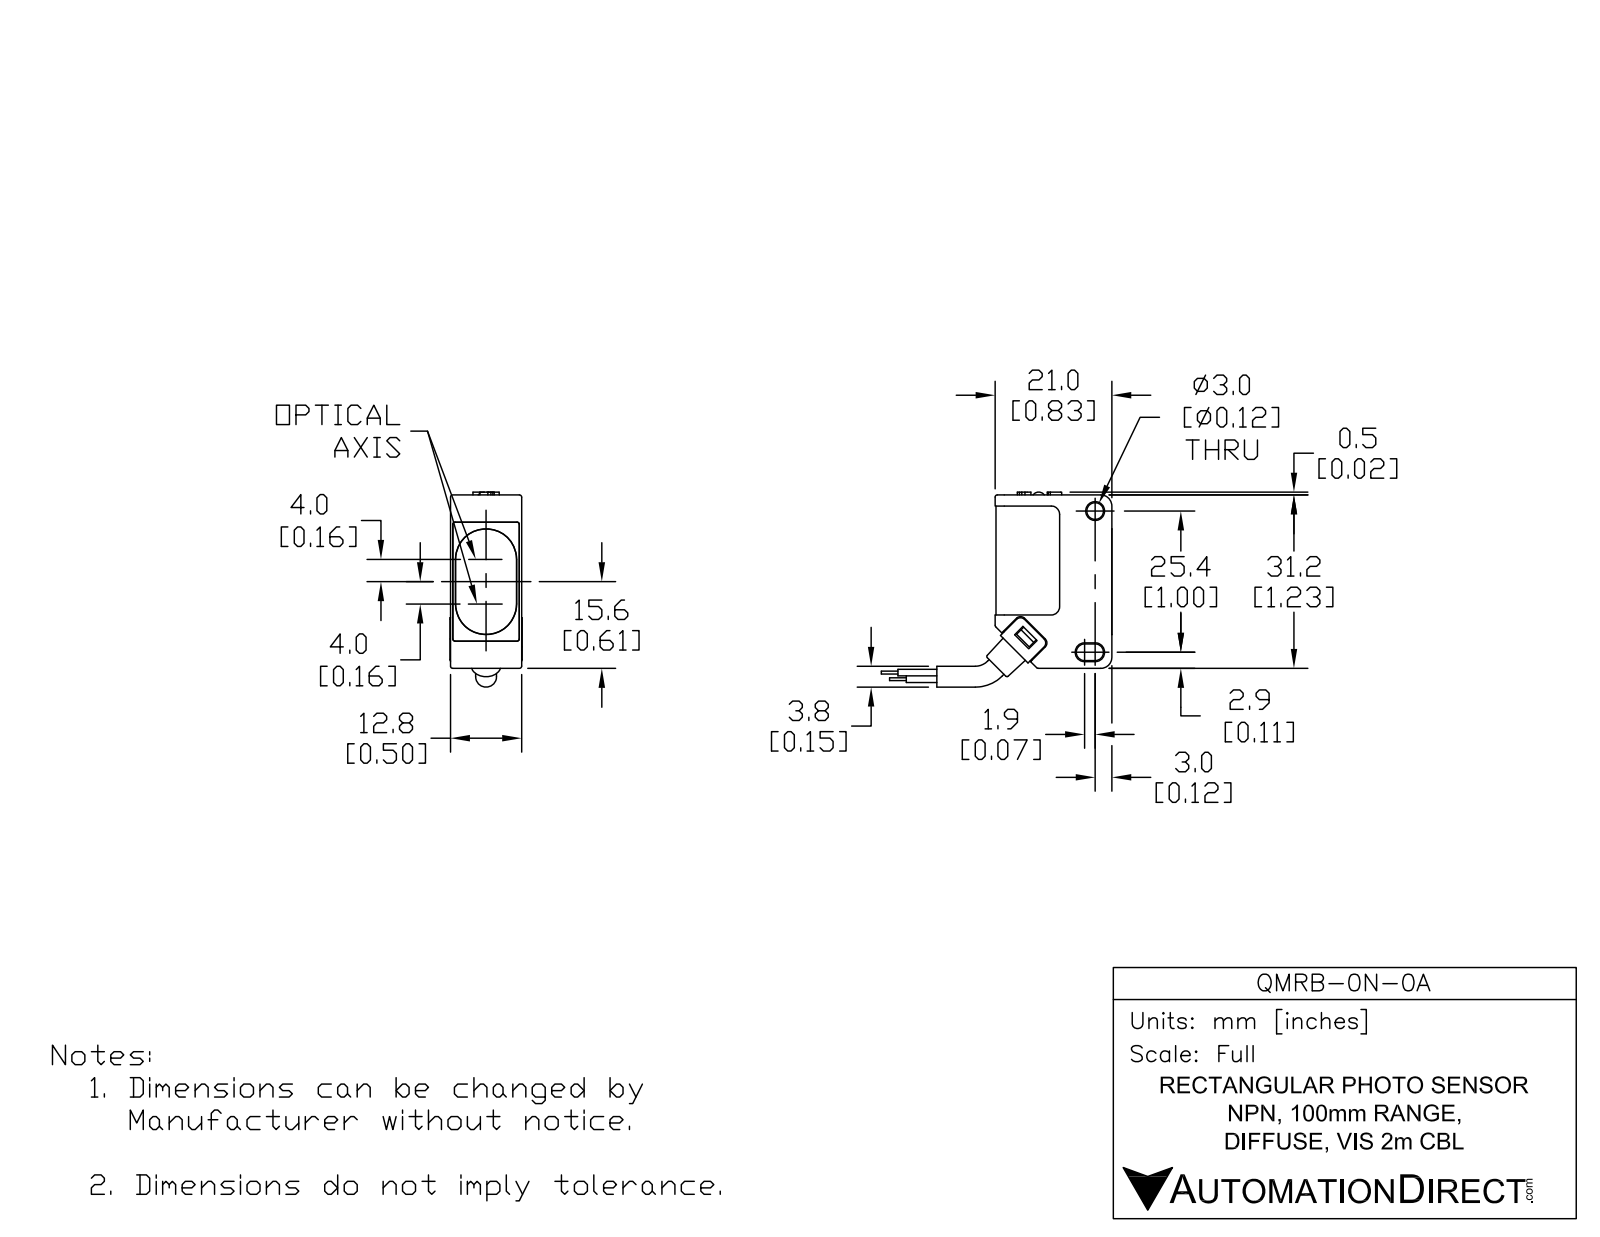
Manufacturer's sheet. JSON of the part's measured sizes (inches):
{"part_name": "QMRB-0N-0A", "step_written_by": "SolidWorks 2017 (AUTOMOTIVE_DESIGN)", "units": "inches", "bodies": {"solids": 9, "faces": 258, "planar": 134, "cylindrical": 100, "other": 24}, "overall_size": [3.193, 1.032, 0.512], "volume_in3": 0.47, "surface_area_in2": 8.375, "round_holes": [[0.118, 3], [0.148, 1], [0.224, 1], [0.283, 1]], "round_bosses_or_shafts": [[0.138, 2]], "partial_cylinders_radius": [[0.016, 13], [0.02, 10], [0.039, 8], [0.059, 6], [0.024, 4], [0.006, 2], [0.035, 2], [0.044, 2]], "face_to_face_distances": [0.02, 0.498, 0.059, 0.016, 0.504, 0.138, 0.488, 0.079, 0.482, 0.492], "hole_center_spacings": [0.205]}
